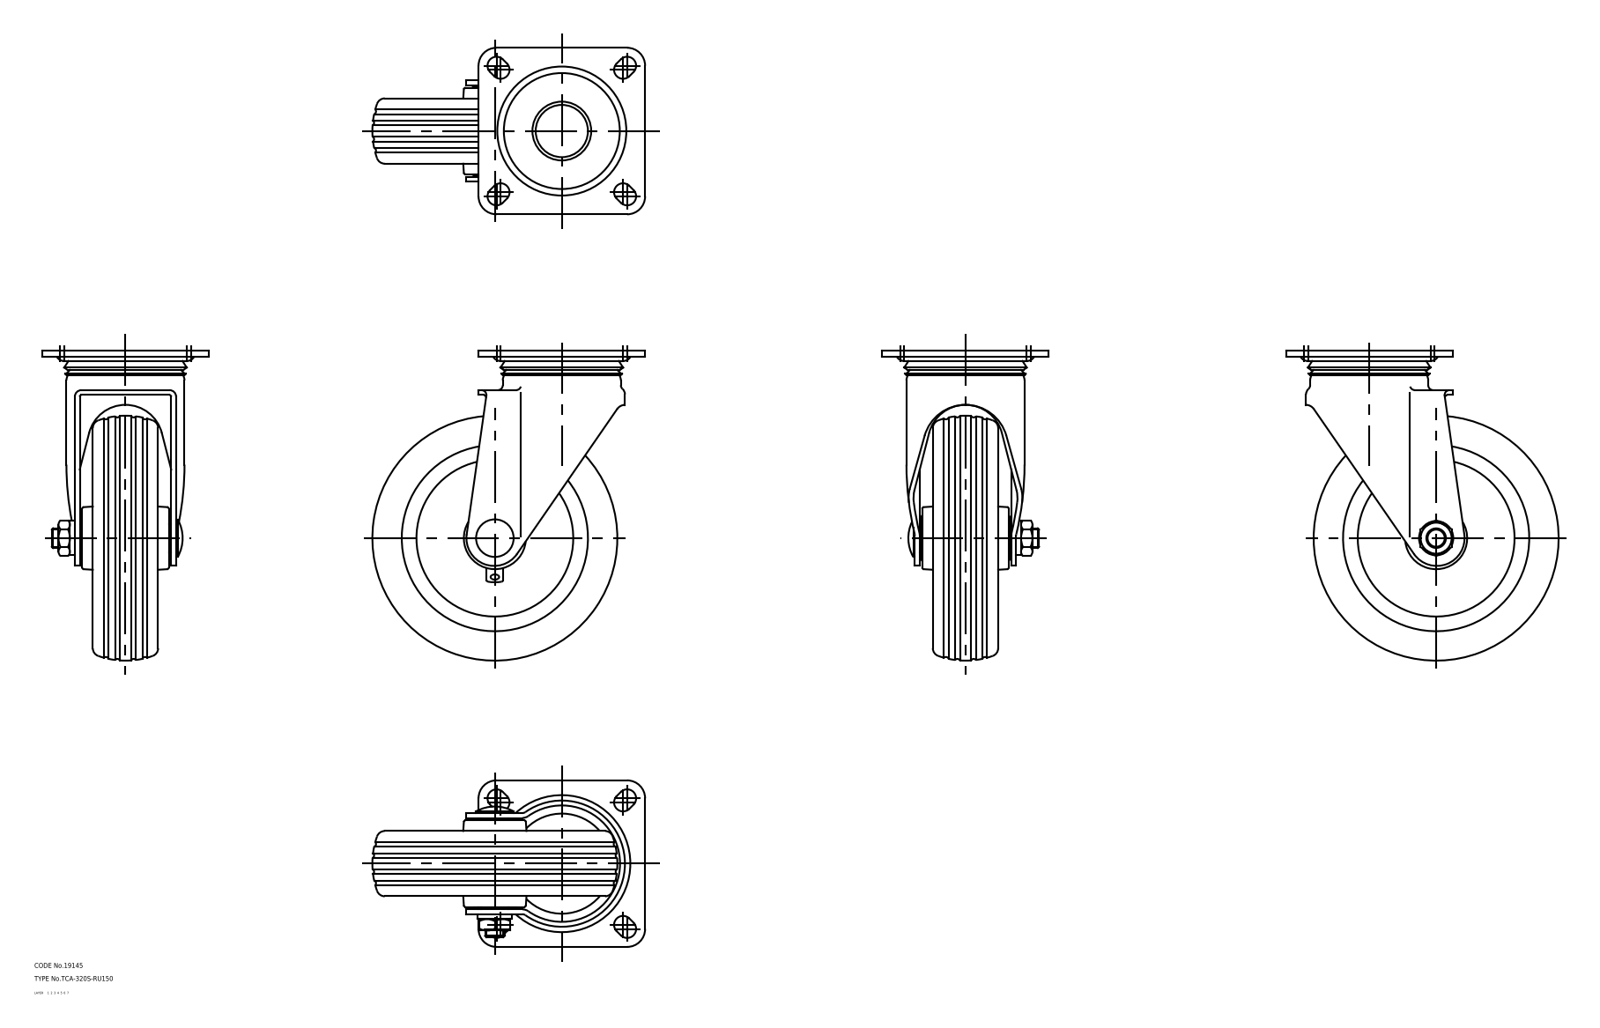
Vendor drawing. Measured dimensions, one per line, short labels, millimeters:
name: 67130767; 67130780; 67130793; 67130806 (+1 more)
written by: CADfix (AUTOMOTIVE_DESIGN)
unit: mm
bodies: 5 solids, 279 faces (0 planar, 0 cylindrical, 279 other)
size: 190 × 167 × 102
volume: 756 843 mm³; area: 136 538 mm²
